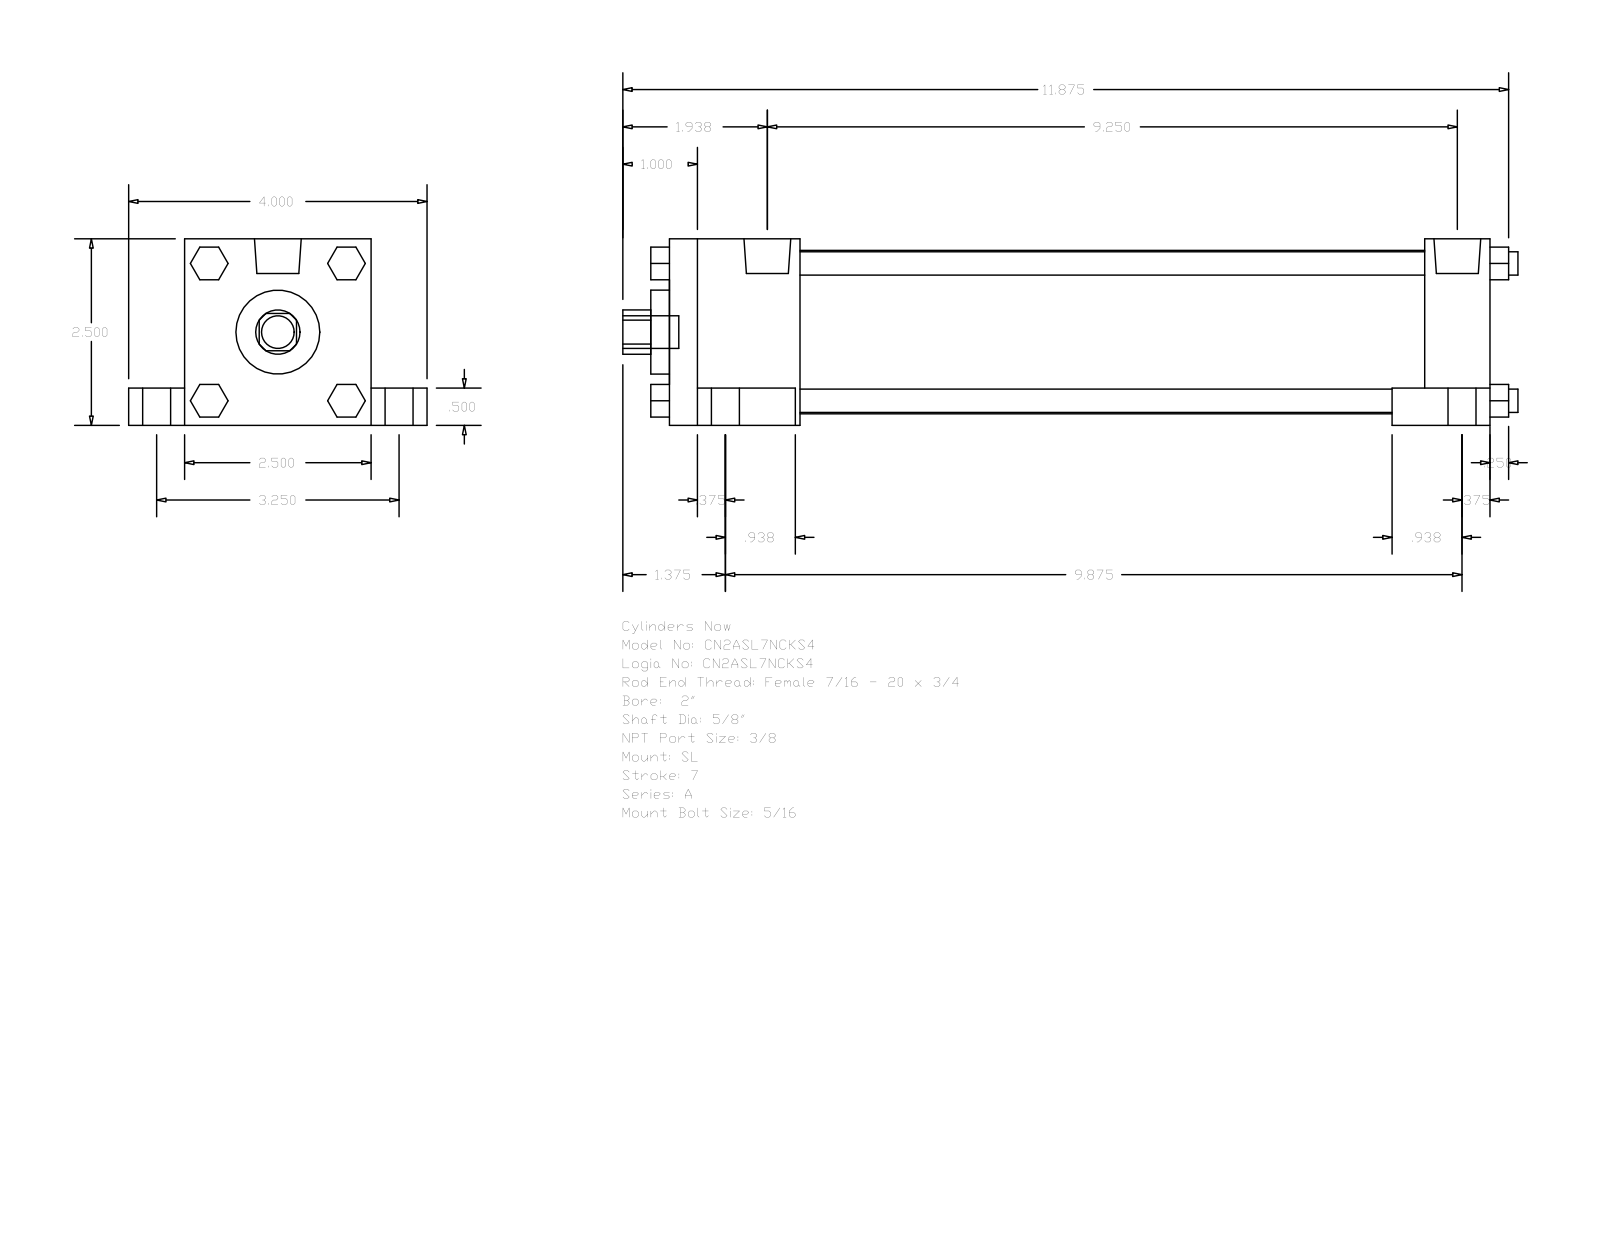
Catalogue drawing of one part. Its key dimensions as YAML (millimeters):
part_name: "A_SL__0200_0.625"
step_written_by: "GSSL Pune (CONFIG_CONTROL_DESIGN)"
units: millimeters
bodies: {solids: 0, faces: 148, planar: 112, cylindrical: 36, other: 0}
overall_size: [304.8, 101.6, 63.5]
round_holes:
  - {diameter: 15.88, count: 1}
  - {diameter: 28.57, count: 1}
  - {diameter: 55.63, count: 1}
round_bosses_or_shafts:
  - {diameter: 15.88, count: 4}
  - {diameter: 9.53, count: 4}
  - {diameter: 7.94, count: 4}
  - {diameter: 5.56, count: 4}
  - {diameter: 15.93, count: 2}
  - {diameter: 11.11, count: 1}
partial_cylinders:
  - {radius: 7.54, count: 1}
face_to_face_distances: [63.5, 279.39, 50.8, 12.7, 19.05, 82.55, 44.45, 234.94, 257.17, 212.72]
